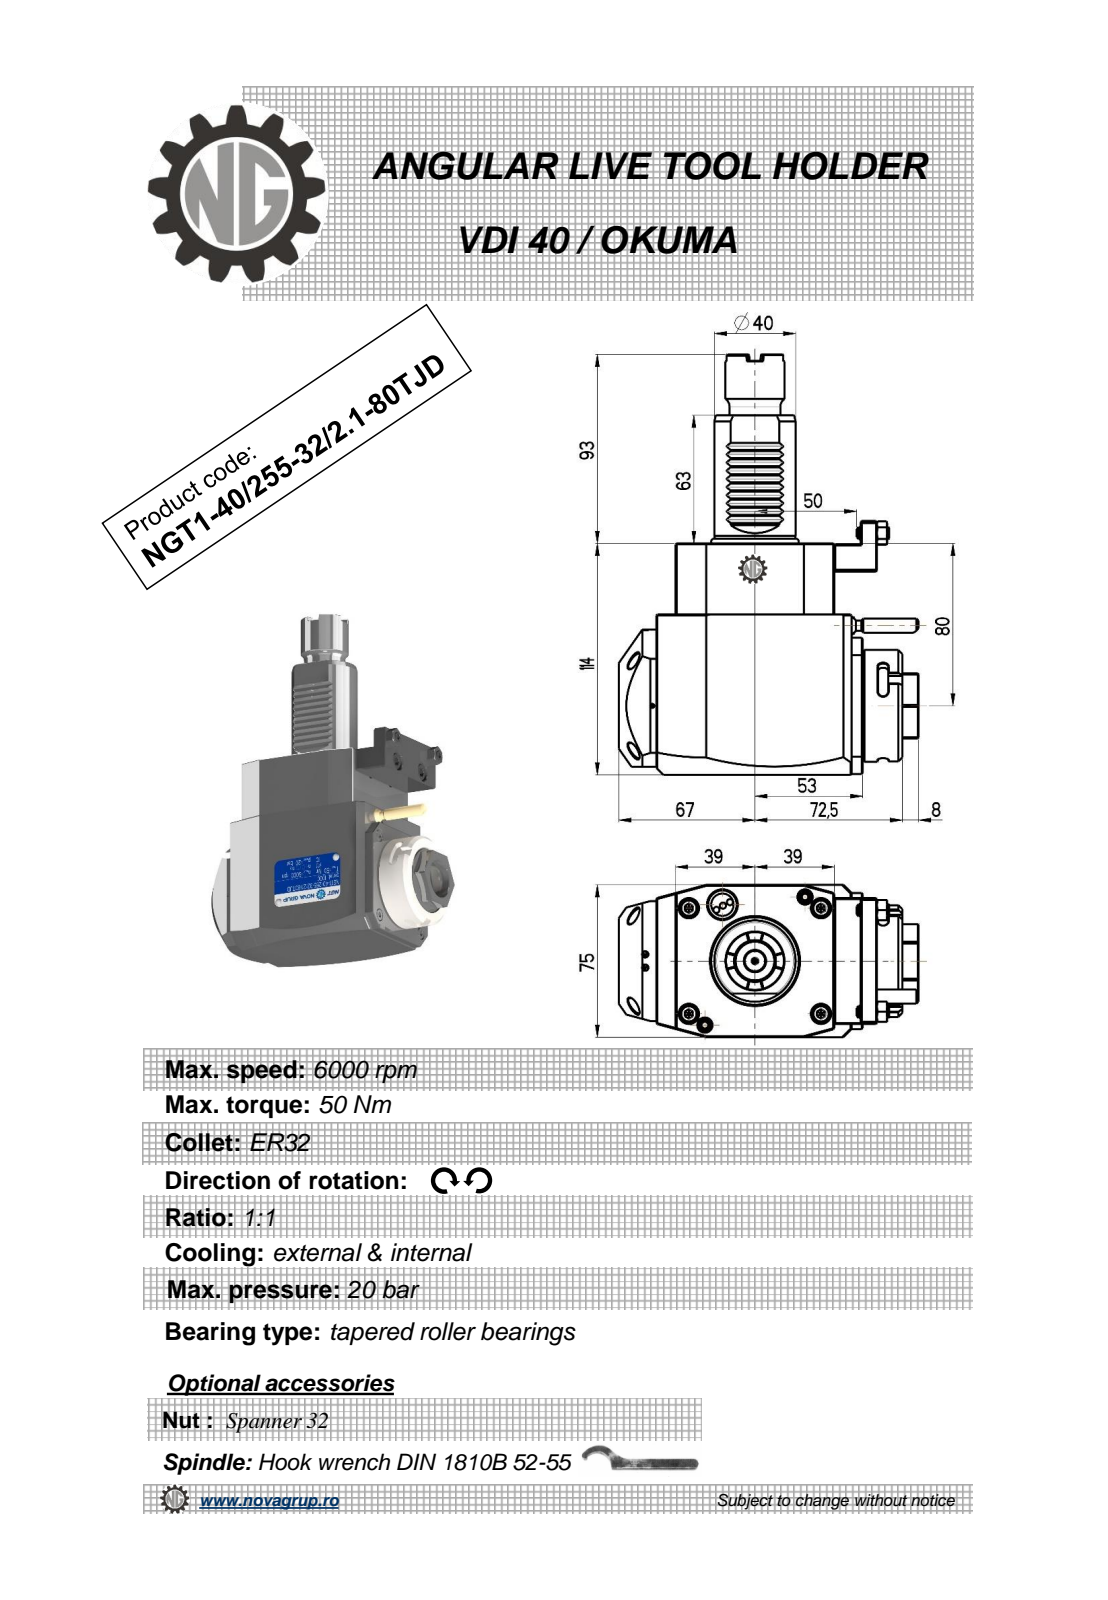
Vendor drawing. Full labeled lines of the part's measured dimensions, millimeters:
Part name (STEP PRODUCT): NGT1_40_255_32_1_1_80TJD
STEP written by: PRO/ENGINEER BY PARAMETRIC TECHNOLOGY CORPORATION, 2010280 (CONFIG_CONTROL_DESIGN)
Units: millimetres
Bodies: 1 solid, 398 faces (200 planar, 70 cylindrical, 128 other)
Overall size (bounding box): 207 × 147.5 × 75
Volume: 994 735 mm³ · Surface area: 76 346 mm²
Round holes (diameter × count): ⌀2.5 ×1, ⌀3 ×1, ⌀23 ×1
Round bosses / shafts (diameter × count): ⌀6 ×2, ⌀55 ×1, ⌀48 ×1, ⌀40 ×1, ⌀29 ×1, ⌀25 ×1, ⌀8.96 ×1, ⌀7 ×1
Partial cylindrical surfaces — rounded edges, fillets, slot ends (radius × count): R0.3 ×10, R0.31 ×10, R2.5 ×6, R180 ×2, R0.5 ×1, R10 ×1, R24.5 ×1, R37.5 ×1
Main face-to-face distances: 75, 114, 14, 21, 92, 12.5, 0.5, 111.5, 19.5, 7
Hole centre spacings: 43.2
